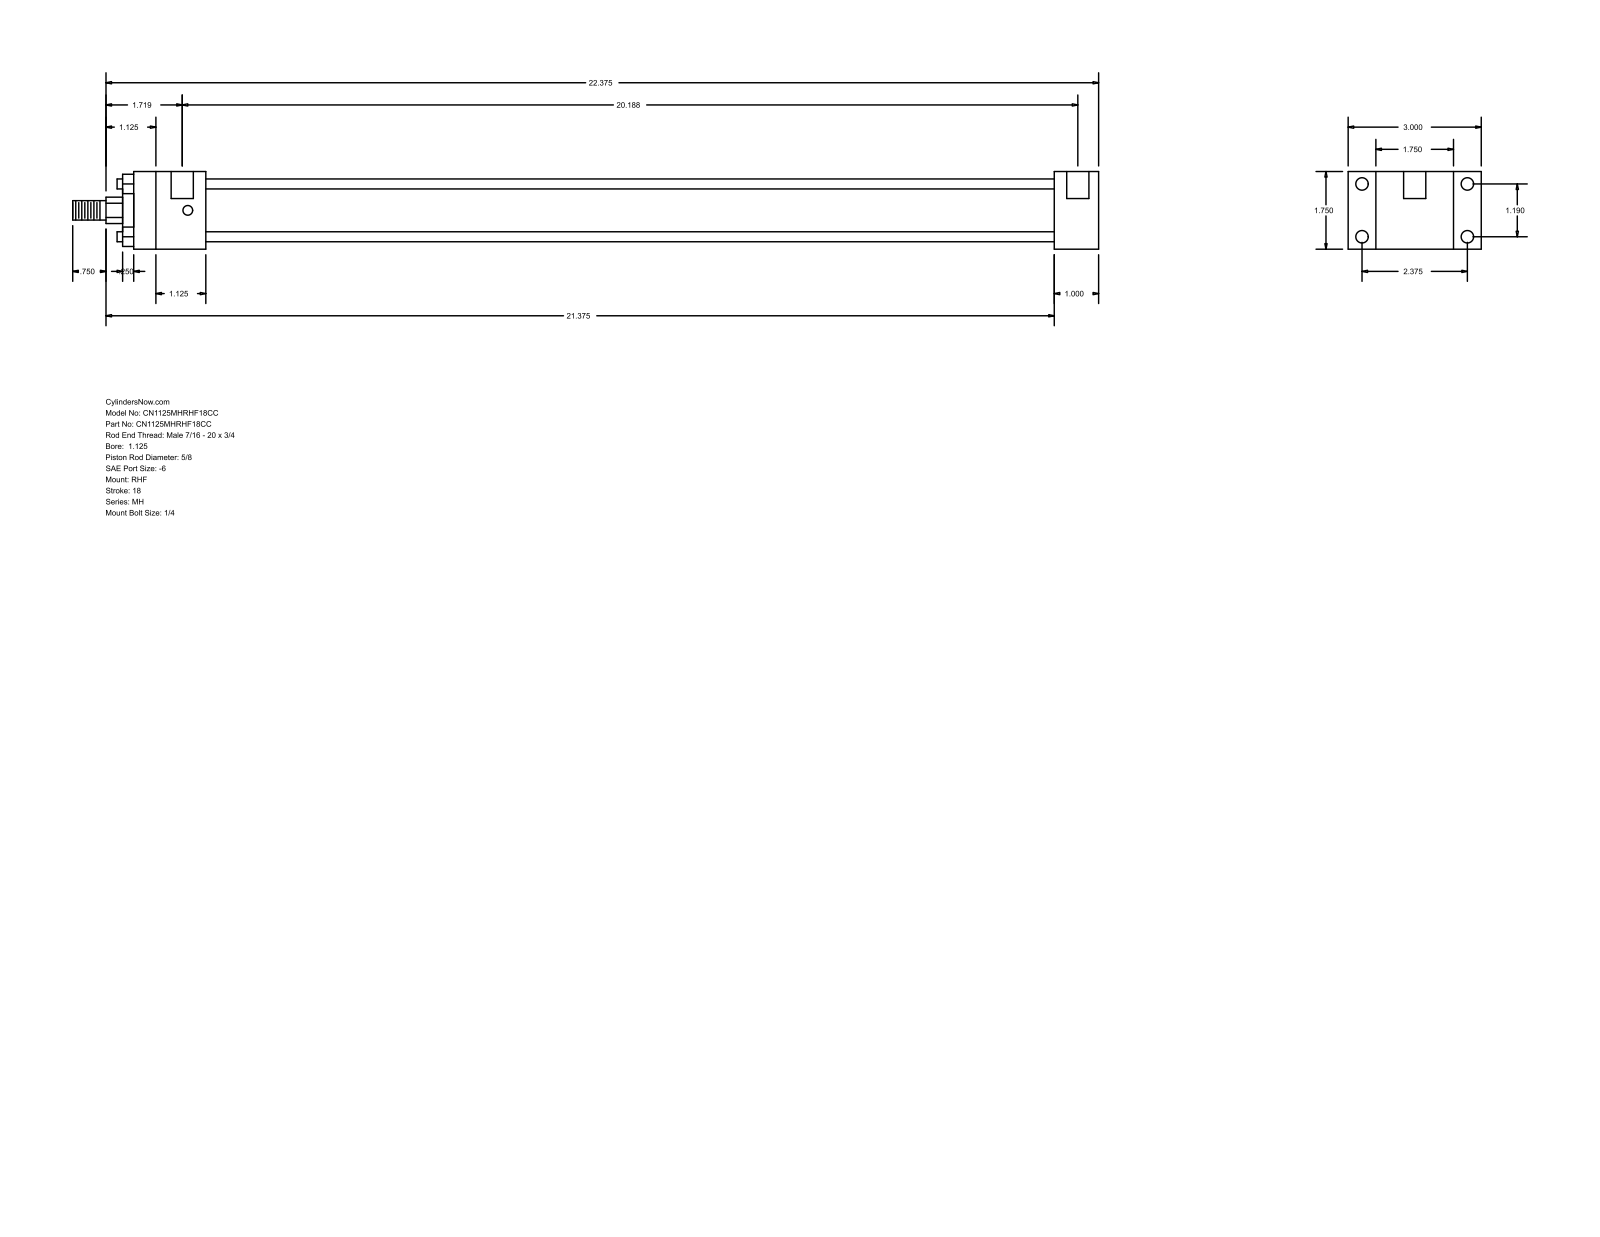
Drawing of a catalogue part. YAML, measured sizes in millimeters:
part_name: "MH_RHF__0112_0.625"
step_written_by: "GSSL Pune (CONFIG_CONTROL_DESIGN)"
units: millimeters
bodies: {solids: 0, faces: 88, planar: 60, cylindrical: 28, other: 0}
overall_size: [587.38, 76.2, 44.45]
round_holes:
  - {diameter: 5.56, count: 4}
  - {diameter: 7.14, count: 4}
  - {diameter: 12.7, count: 2}
round_bosses_or_shafts:
  - {diameter: 5.71, count: 4}
  - {diameter: 34.92, count: 1}
  - {diameter: 28.57, count: 1}
  - {diameter: 15.88, count: 1}
  - {diameter: 11.11, count: 1}
partial_cylinders:
  - {radius: 7.54, count: 1}
face_to_face_distances: [44.46, 15.87, 60.33, 25.41, 76.2, 485.77, 511.18, 41.27, 527.04, 552.45]
hole_center_spacings: [30.22, 60.32, 67.47, 509.59, 3.17, 512.76]
